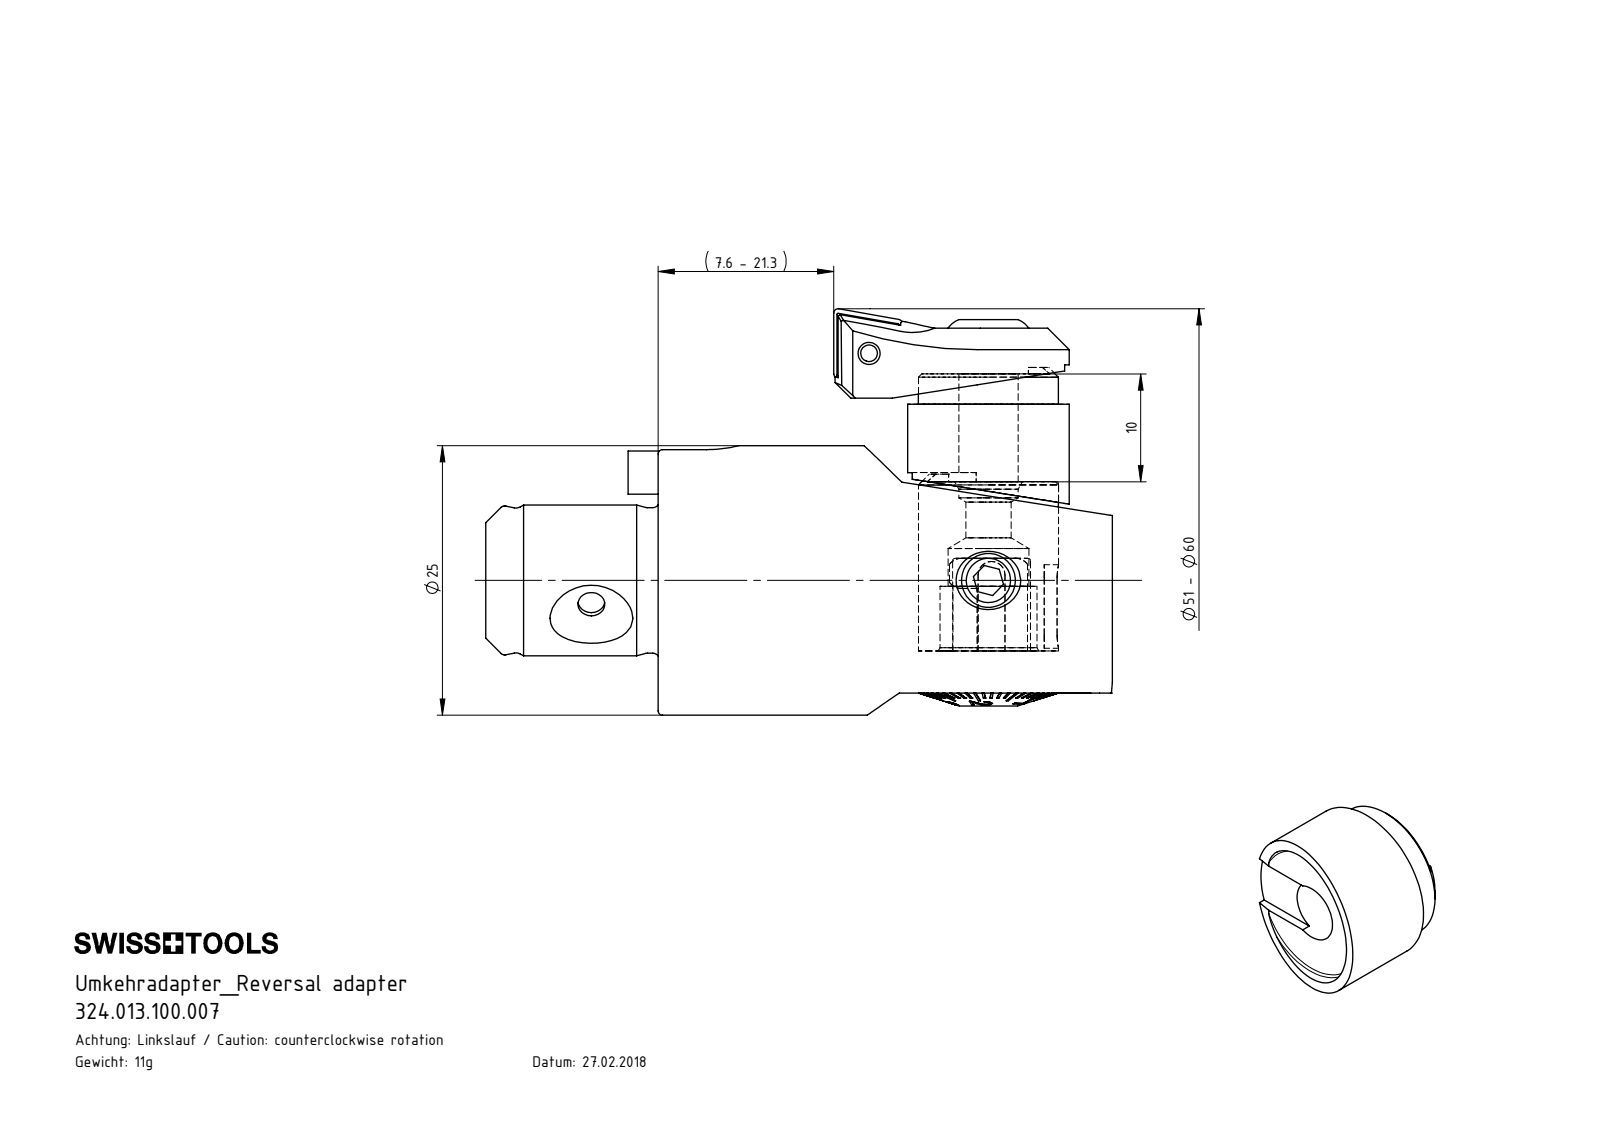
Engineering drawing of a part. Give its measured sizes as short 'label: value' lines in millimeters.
name: 324.013.100.007; F25-U00.001.010_B
written by: SolidWorks 2017 (CONFIG_CONTROL_DESIGN)
unit: mm
bodies: 1 solid, 27 faces (11 planar, 11 cylindrical, 5 other)
size: 15 × 15 × 12.68
volume: 1 429 mm³; area: 1 009 mm²
holes: 1× ⌀5.5, 1× ⌀13
bosses: 1× ⌀15
rounds: 2× R0.5
face distances: 10, 2.8, 7.2, 9.15, 6.35, 0.85, 0.6, 3.4, 9.75, 10.6
